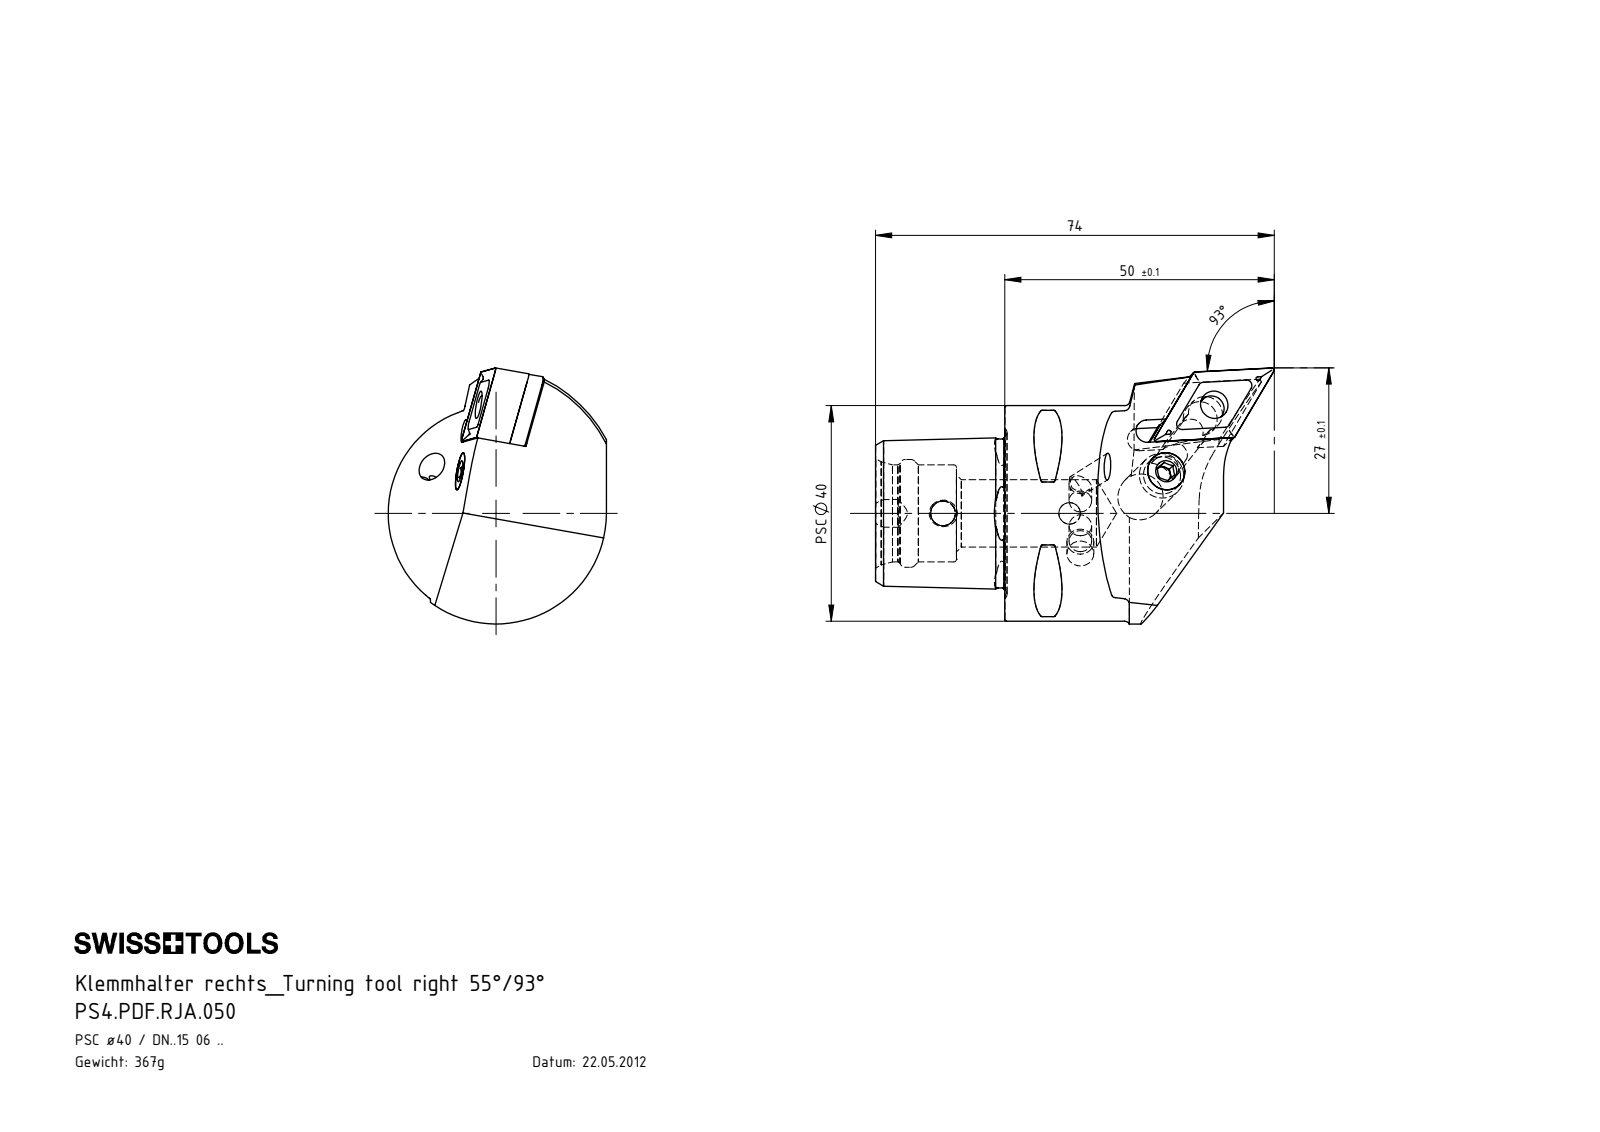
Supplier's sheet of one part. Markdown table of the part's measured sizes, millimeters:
| quantity | value |
| --- | --- |
| part name | PS4-PDF.RJA.050; KVT_MB_600_050; WCD-ER1.101.000; DNMG150604 (+4 more) |
| STEP written by | SolidWorks 2012 (CONFIG_CONTROL_DESIGN) |
| units | millimeters |
| bodies | 8 solids, 352 faces (90 planar, 85 cylindrical, 177 other) |
| overall size | 74 × 47.5 × 40.5 |
| volume | 47 672 mm³ |
| surface area | 15 573 mm² |
| round holes (diameter × count) | 4 × 2, 4.2 × 2, 4.6 × 1, 5 × 1, 5.16 × 1, 6.4 × 1, 7 × 1, 8.4 × 1, 12.5 × 1, 18 × 1, 20 × 1 |
| round bosses / shafts (diameter × count) | 40 × 1, 8 × 1, 7.9 × 1, 6.4 × 1, 5 × 1, 4.7 × 1, 3.55 × 1 |
| partial cylindrical surfaces (radius × count) | 0.3 × 8, 0.4 × 4, 1 × 4, 2.5 × 2, 0.8 × 1, 2.1 × 1, 2.35 × 1, 2.8 × 1 |
| main face-to-face distances | 6.05, 3.18, 9.23, 12.7, 12.69, 24, 4.85, 15.52, 12.3, 5.6 |
| hole center spacings | 15.6, 23.5 |
